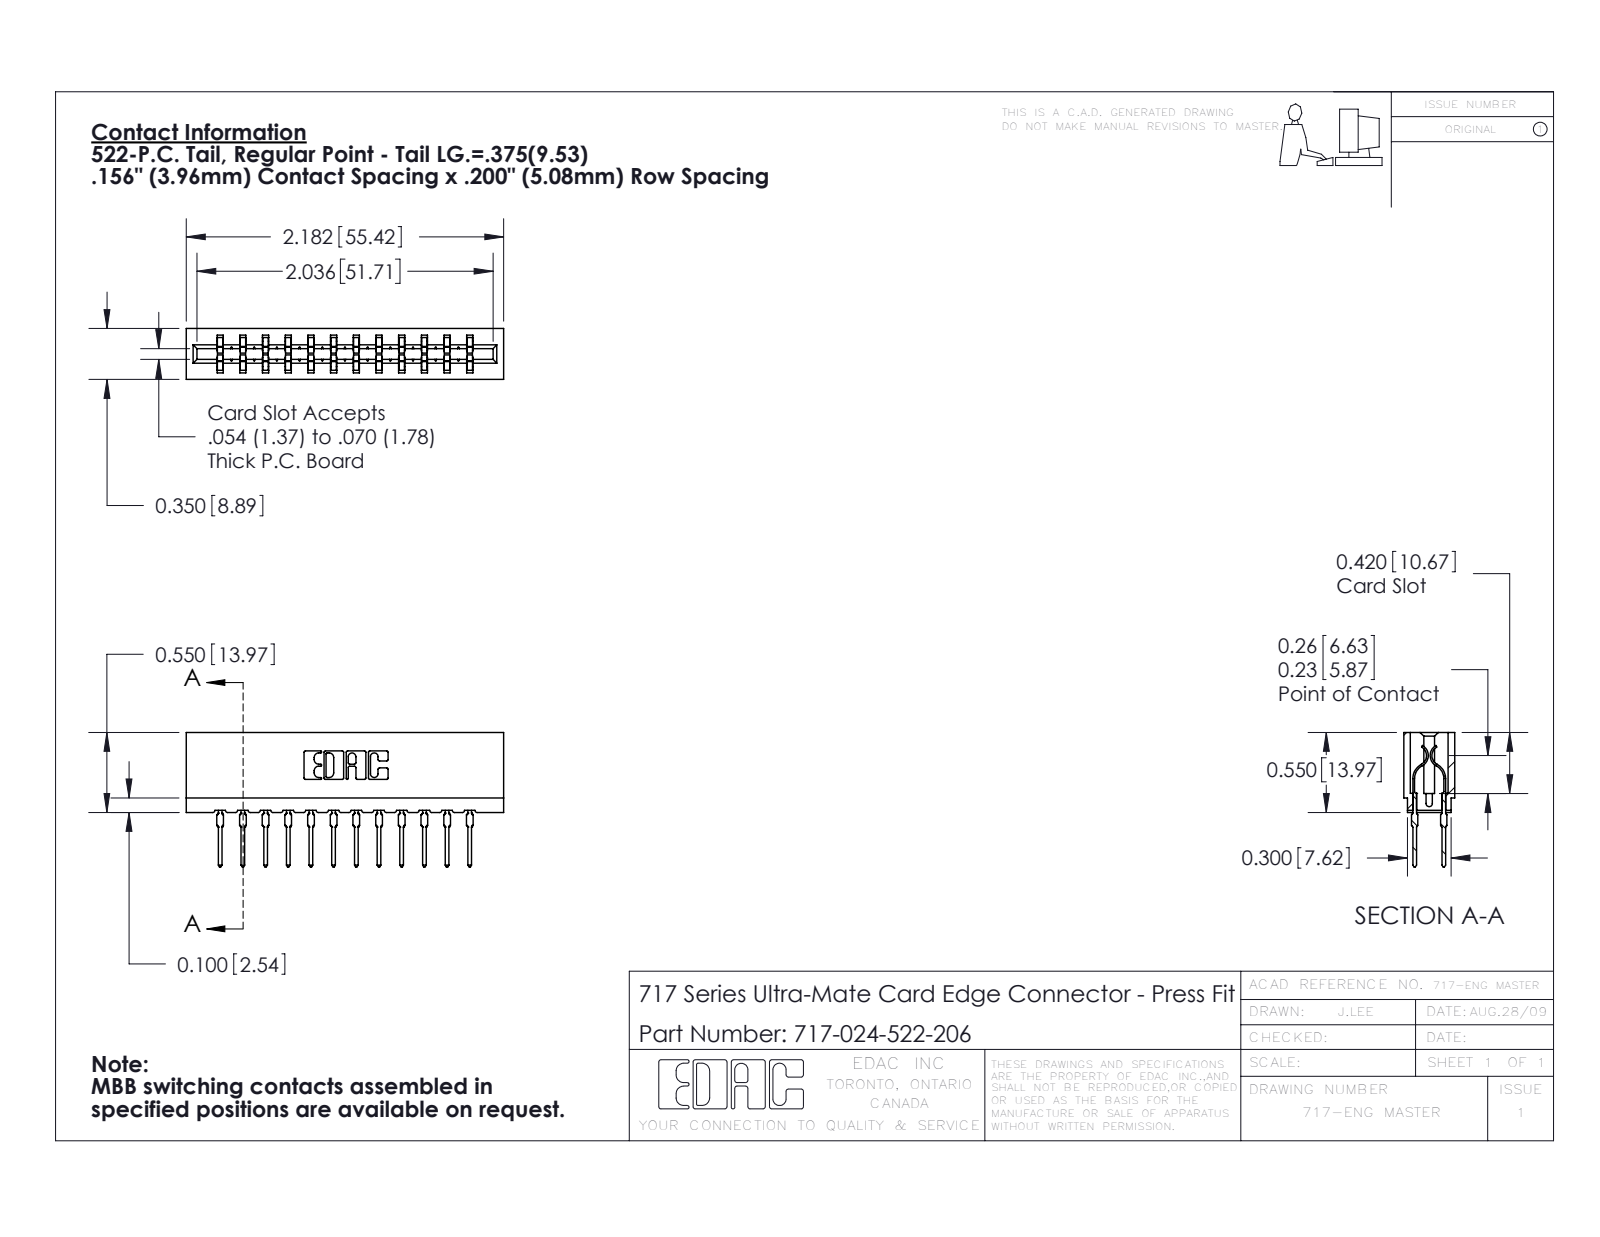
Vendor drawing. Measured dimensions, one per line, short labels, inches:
name: 745-292-001_522; 717-024-522-206; 717 Part_Insulator Option - 06
written by: SolidWorks 2016 (CONFIG_CONTROL_DESIGN)
unit: in
bodies: 25 solids, 2254 faces (1170 planar, 460 cylindrical, 624 other)
size: 2.182 × 0.924 × 0.35
volume: 0.302 in³; area: 11.26 in²
rounds: 48× R0.021, 24× R0.015, 22× R0.01, 8× R0.005, 8× R0.011, 6× R0.007, 6× R0.031, 3× R0.026
face distances: 0.212, 0.138, 0.156, 0.624, 0.35, 0.468, 0.198, 0.312, 0.063, 0.287
